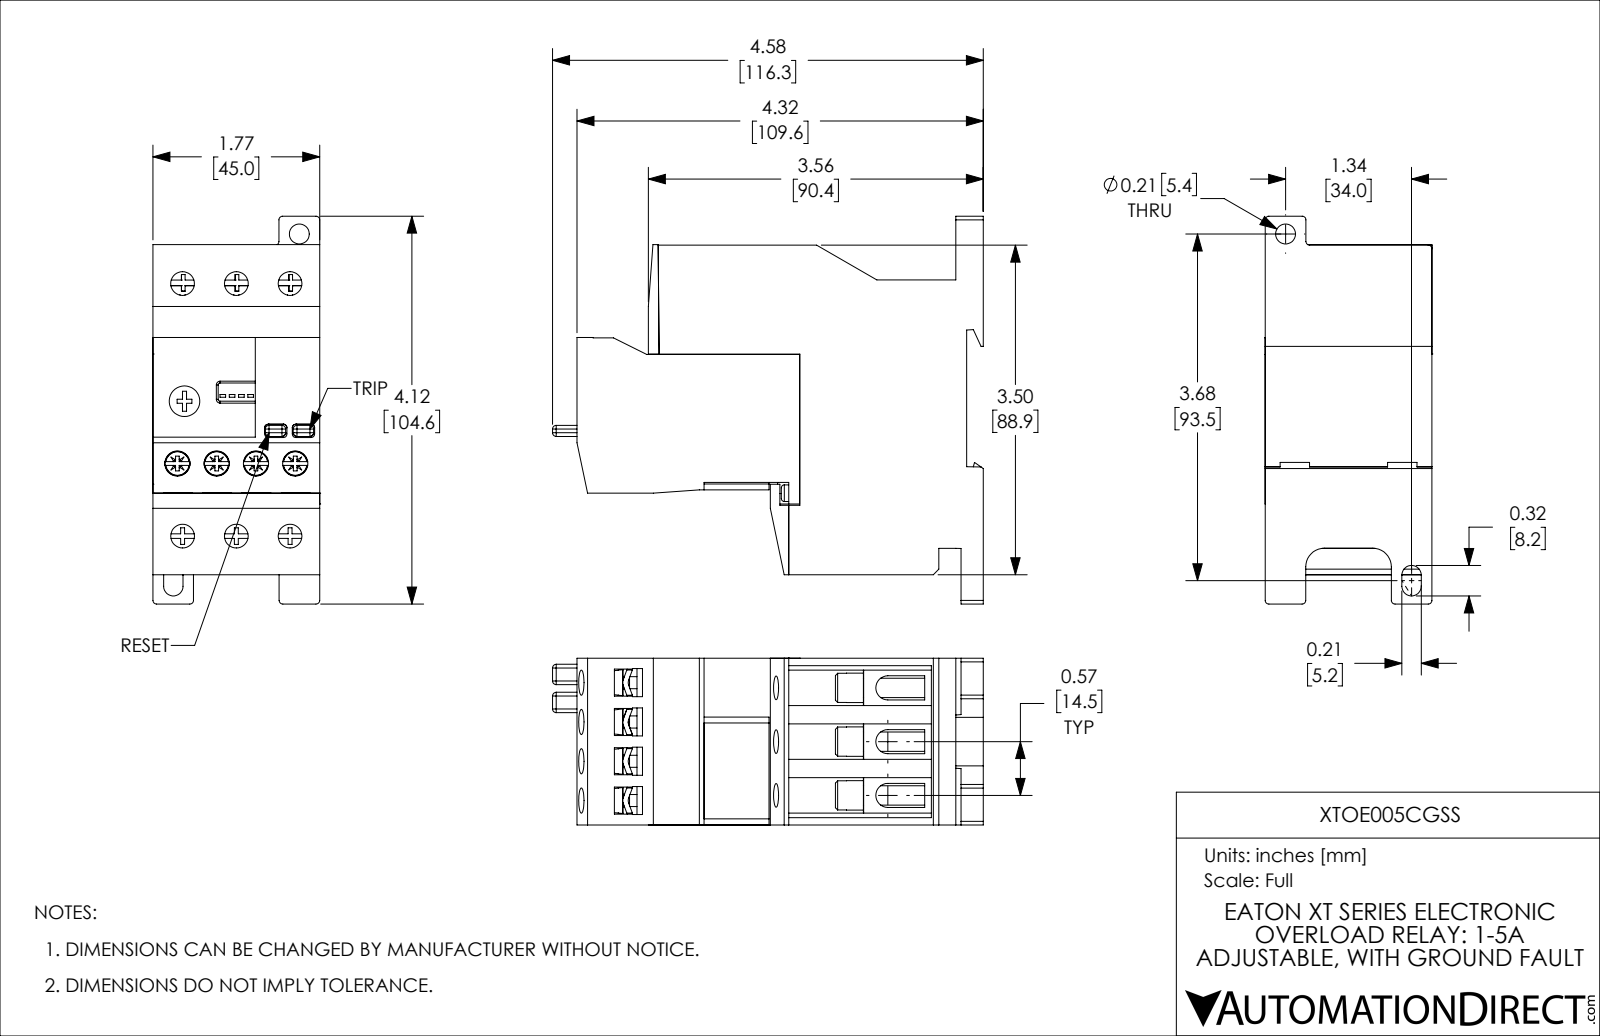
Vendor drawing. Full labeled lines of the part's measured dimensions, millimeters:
Part name (STEP PRODUCT): XTOE005CGSS
STEP written by: SolidWorks 2018 (AUTOMOTIVE_DESIGN)
Units: millimetres
Bodies: 42 solids, 1296 faces (854 planar, 281 cylindrical, 161 other)
Overall size (bounding box): 116.25 × 104.6 × 45.01
Volume: 292 500 mm³ · Surface area: 75 869 mm²
Round holes (diameter × count): ⌀6.4 ×6, ⌀3.55 ×5, ⌀6.8 ×4, ⌀7.94 ×3, ⌀2.18 ×2, ⌀3.2 ×2, ⌀5.38 ×1
Round bosses / shafts (diameter × count): ⌀3.4 ×4, ⌀3.25 ×4, ⌀2.8 ×4, ⌀2.5 ×4, ⌀8 ×3, ⌀4.5 ×2, ⌀8.27 ×1
Partial cylindrical surfaces — rounded edges, fillets, slot ends (radius × count): R0.5 ×64, R0.3 ×24, R1 ×22, R2 ×10, R3.25 ×6, R0.8 ×4, R0.4 ×3, R1.57 ×2
Main face-to-face distances: 45, 14.5, 1.87, 10.89, 4.5, 45.01, 44.99, 29, 49.5, 16.37
Hole centre spacings: 10.6, 21.2, 10.59, 10.61, 19.63, 48.55, 48.82, 51.07
